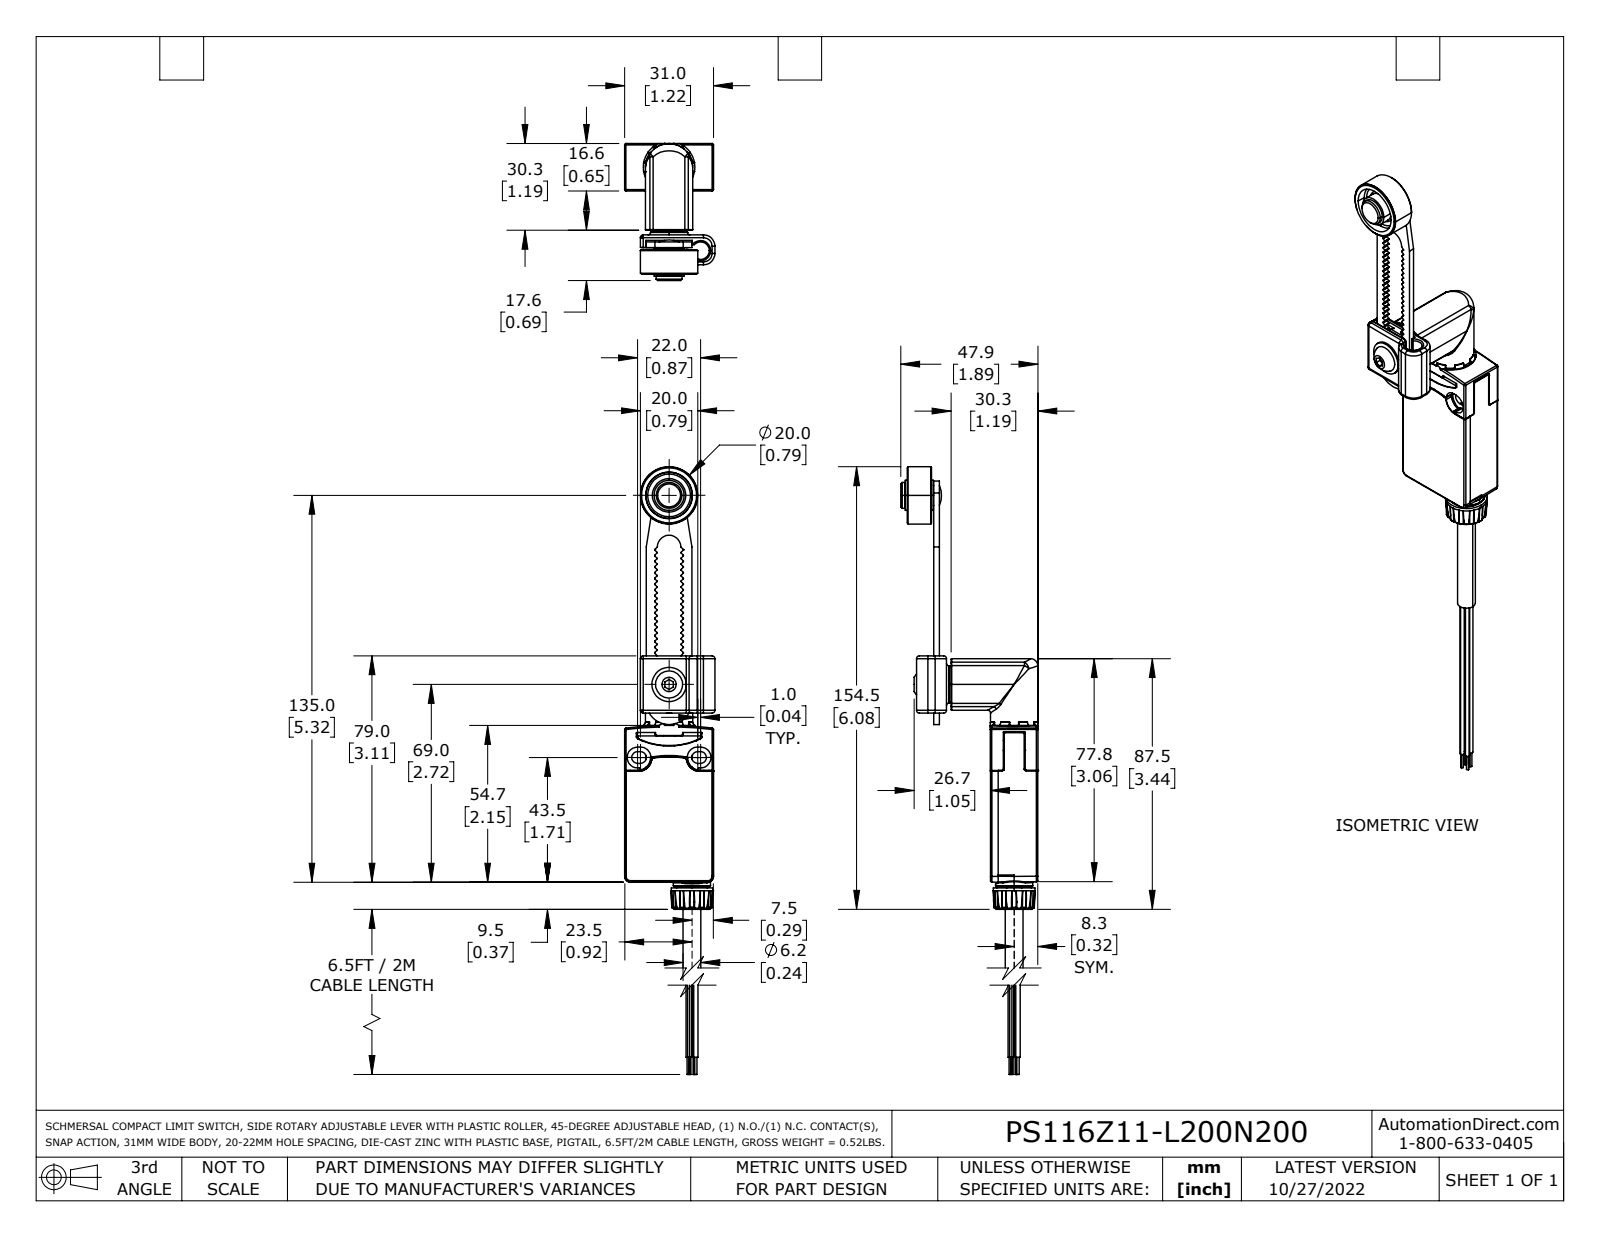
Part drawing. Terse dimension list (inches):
name: PS116Z11-L200N200_Default
written by: SolidWorks 2021 (CONFIG_CONTROL_DESIGN)
unit: in
bodies: 1 solid, 1556 faces (489 planar, 714 cylindrical, 353 other)
size: 10.335 × 1.886 × 1.24
volume: 2.699 in³; area: 34.77 in²
holes: 2× ⌀0.48, 1× ⌀0.079, 1× ⌀0.24, 1× ⌀0.252, 1× ⌀0.315, 1× ⌀0.571, 1× ⌀0.583
bosses: 4× ⌀0.059, 4× ⌀0.031, 2× ⌀0.512, 1× ⌀0.787, 1× ⌀0.65, 1× ⌀0.571, 1× ⌀0.567, 1× ⌀0.524
rounds: 253× R0.008, 61× R0.004, 37× R0.02, 27× R0.039, 12× R0.079, 10× R0.014, 6× R0.012, 5× R0.118
face distances: 0.65, 0.781, 0.079, 1.431, 1.352, 0.703, 0.652, 0.098, 0.177, 0.201
hole spacings: 0.315, 1.154, 1.227, 2.598
